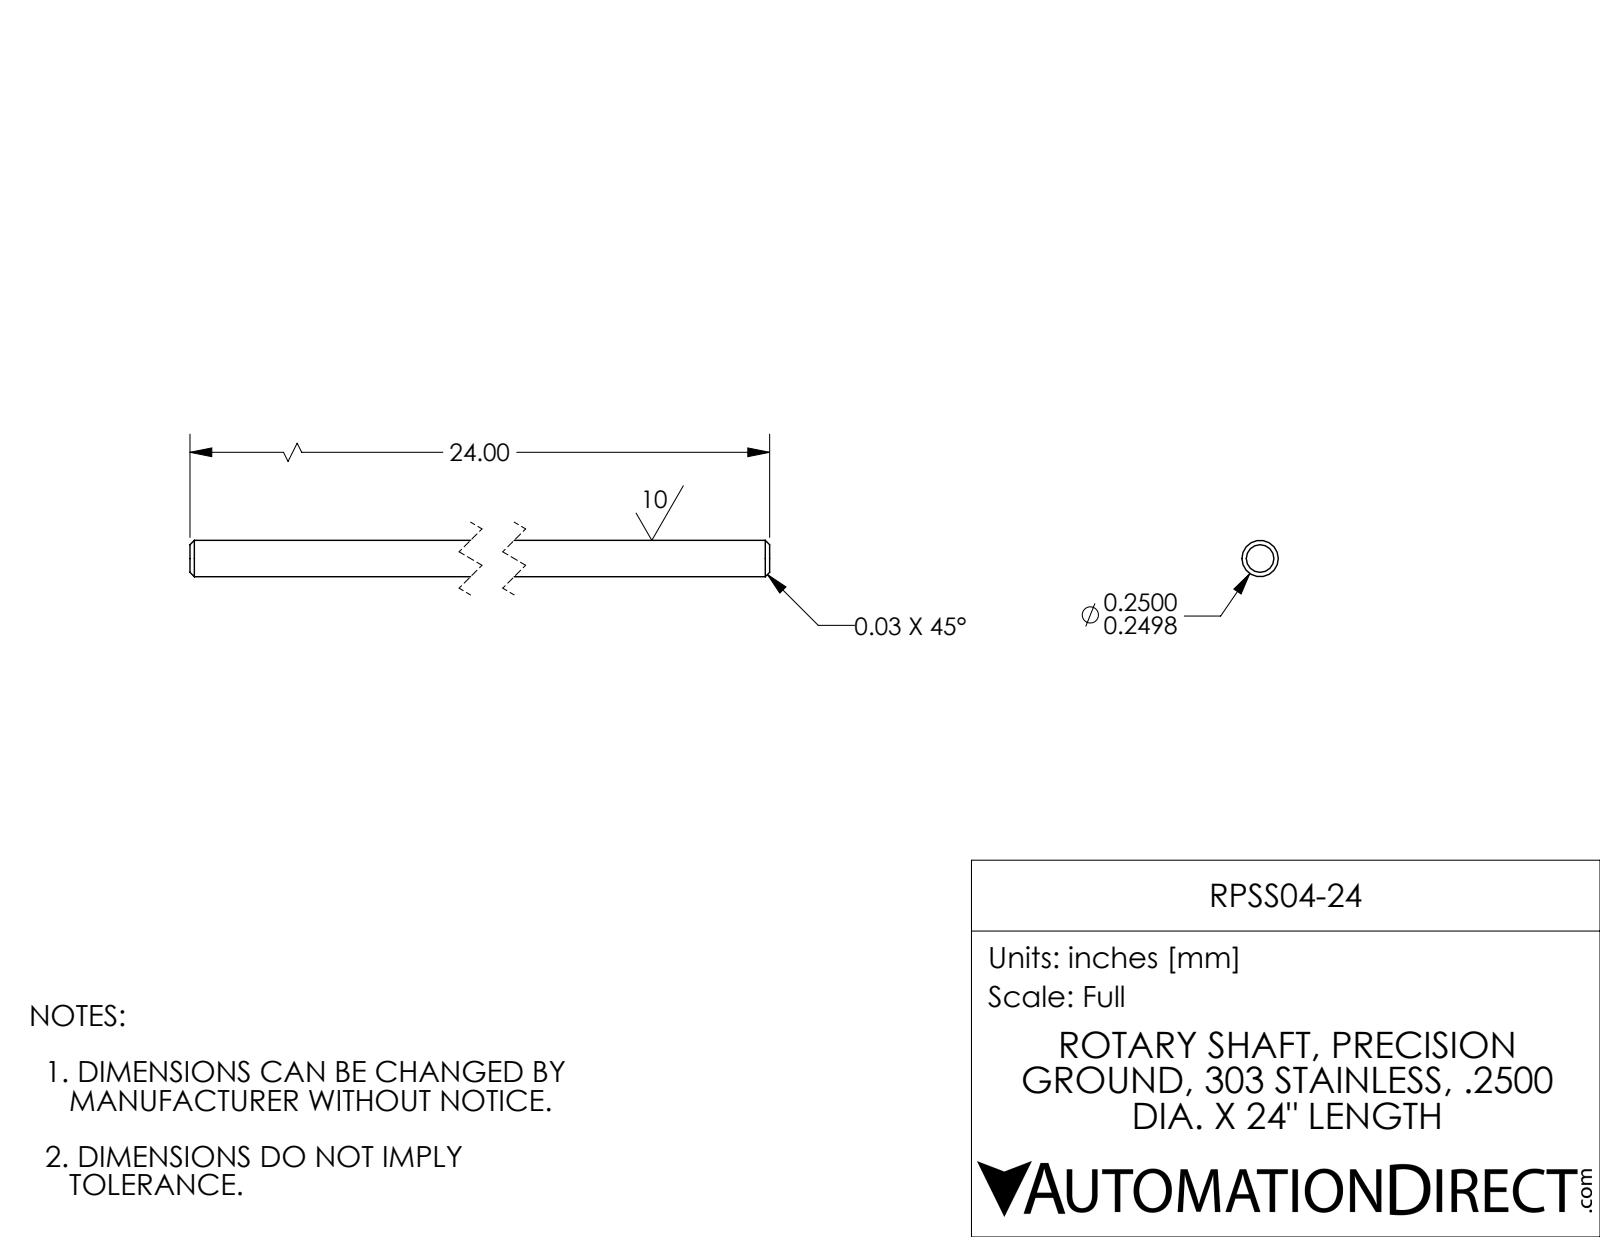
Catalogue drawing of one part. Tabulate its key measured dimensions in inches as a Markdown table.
| quantity | value |
| --- | --- |
| part name | RPSS04-24 |
| STEP written by | SolidWorks 2017 (AUTOMOTIVE_DESIGN) |
| units | inches |
| bodies | 1 solid, 8 faces (2 planar, 2 cylindrical, 4 other) |
| overall size | 24 × 0.25 × 0.25 |
| volume | 1.177 in³ |
| surface area | 18.92 in² |
| round bosses / shafts (diameter × count) | 0.25 × 1 |
| main face-to-face distances | 24 |
